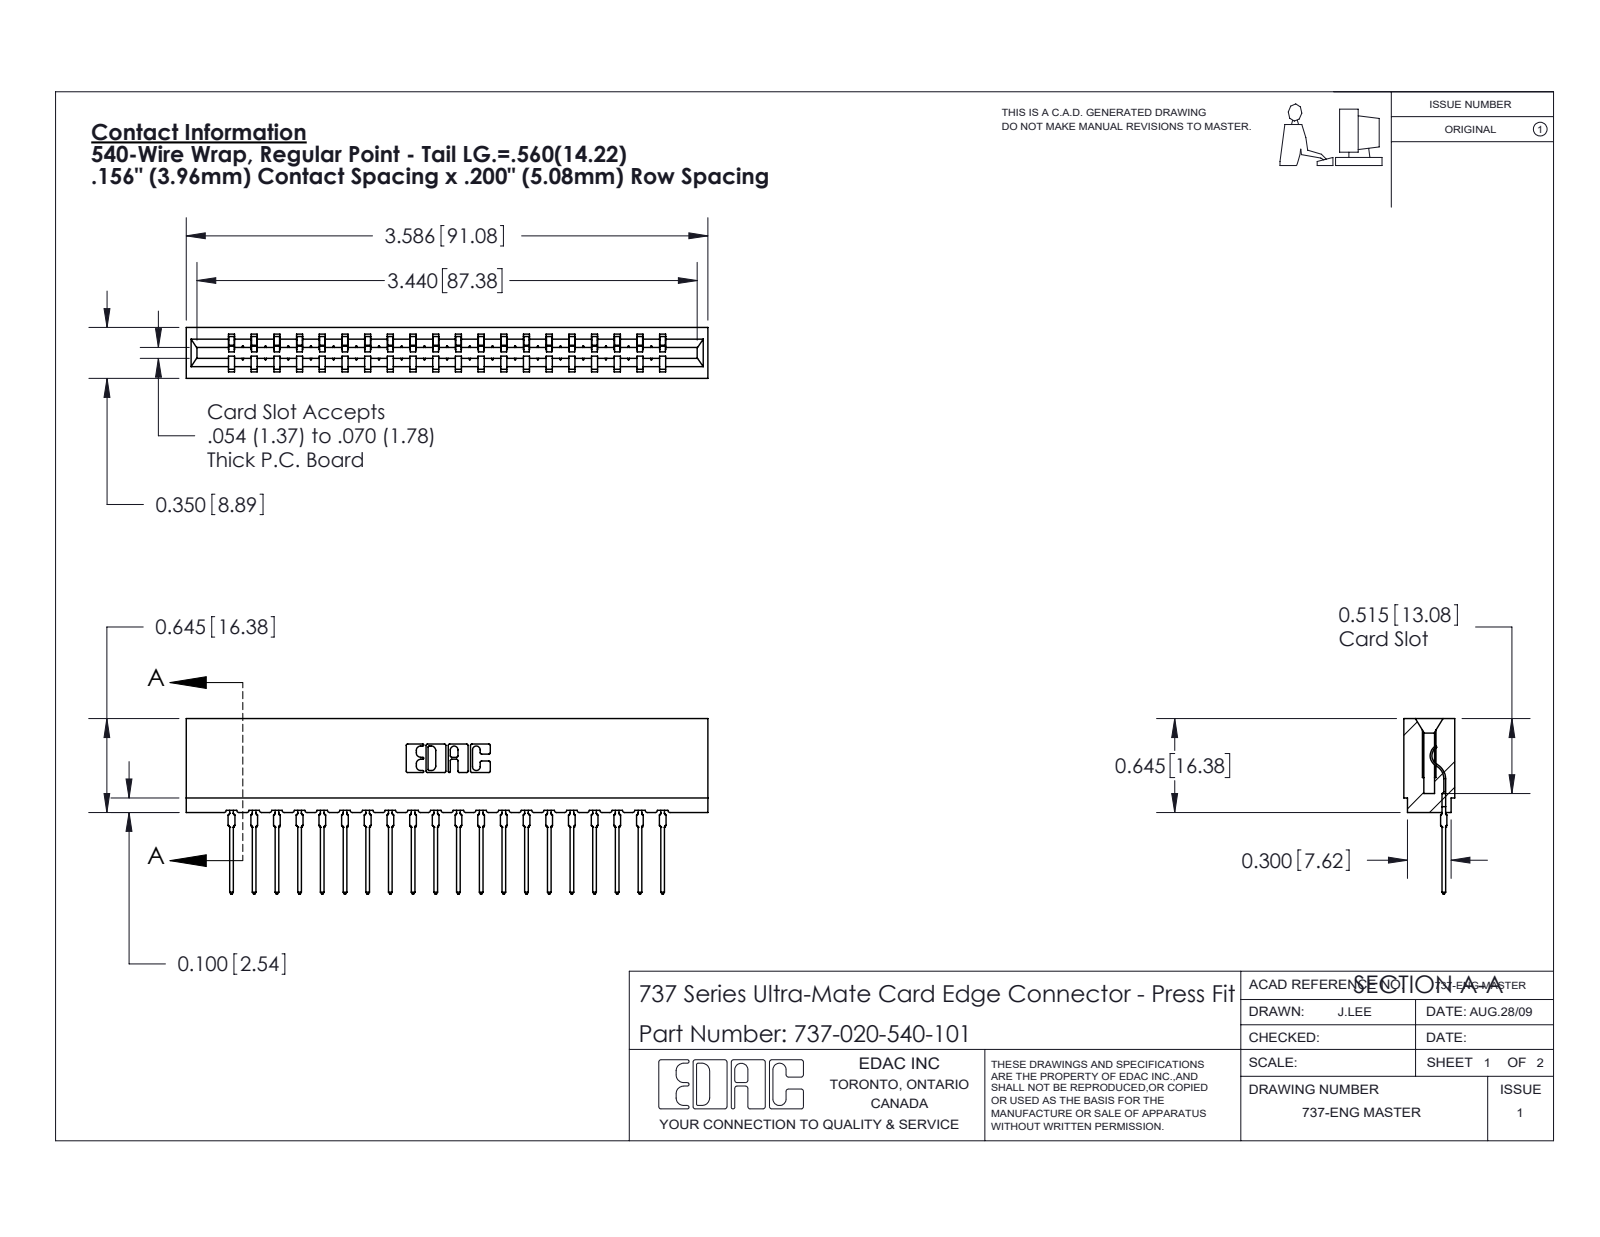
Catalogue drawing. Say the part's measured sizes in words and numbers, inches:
The part is named "737-020-540-101; 745-292-001_540; 737 Part_Insulator Option - 01". Its 3-D file was written by "SolidWorks 2020 (CONFIG_CONTROL_DESIGN)". It is 21 solids with 2354 faces: 1414 planar, 420 cylindrical and 520 other. Overall it measures 3.586 by 1.206 by 0.35 inches. Its volume is 0.55 cubic inches and its surface area 18.5 square inches. Partial cylindrical surfaces (rounded edges, fillets, slot ends): 40 of radius 0.015, 40 of radius 0.021, 22 of radius 0.01, 6 of radius 0.007, 6 of radius 0.031, 4 of radius 0.005, 4 of radius 0.011, 3 of radius 0.026. The main face-to-face distances are 0.138, 0.212, 0.35, 0.156, 0.78, 0.624, 0.074, 0.045, 0.305, 0.093.
